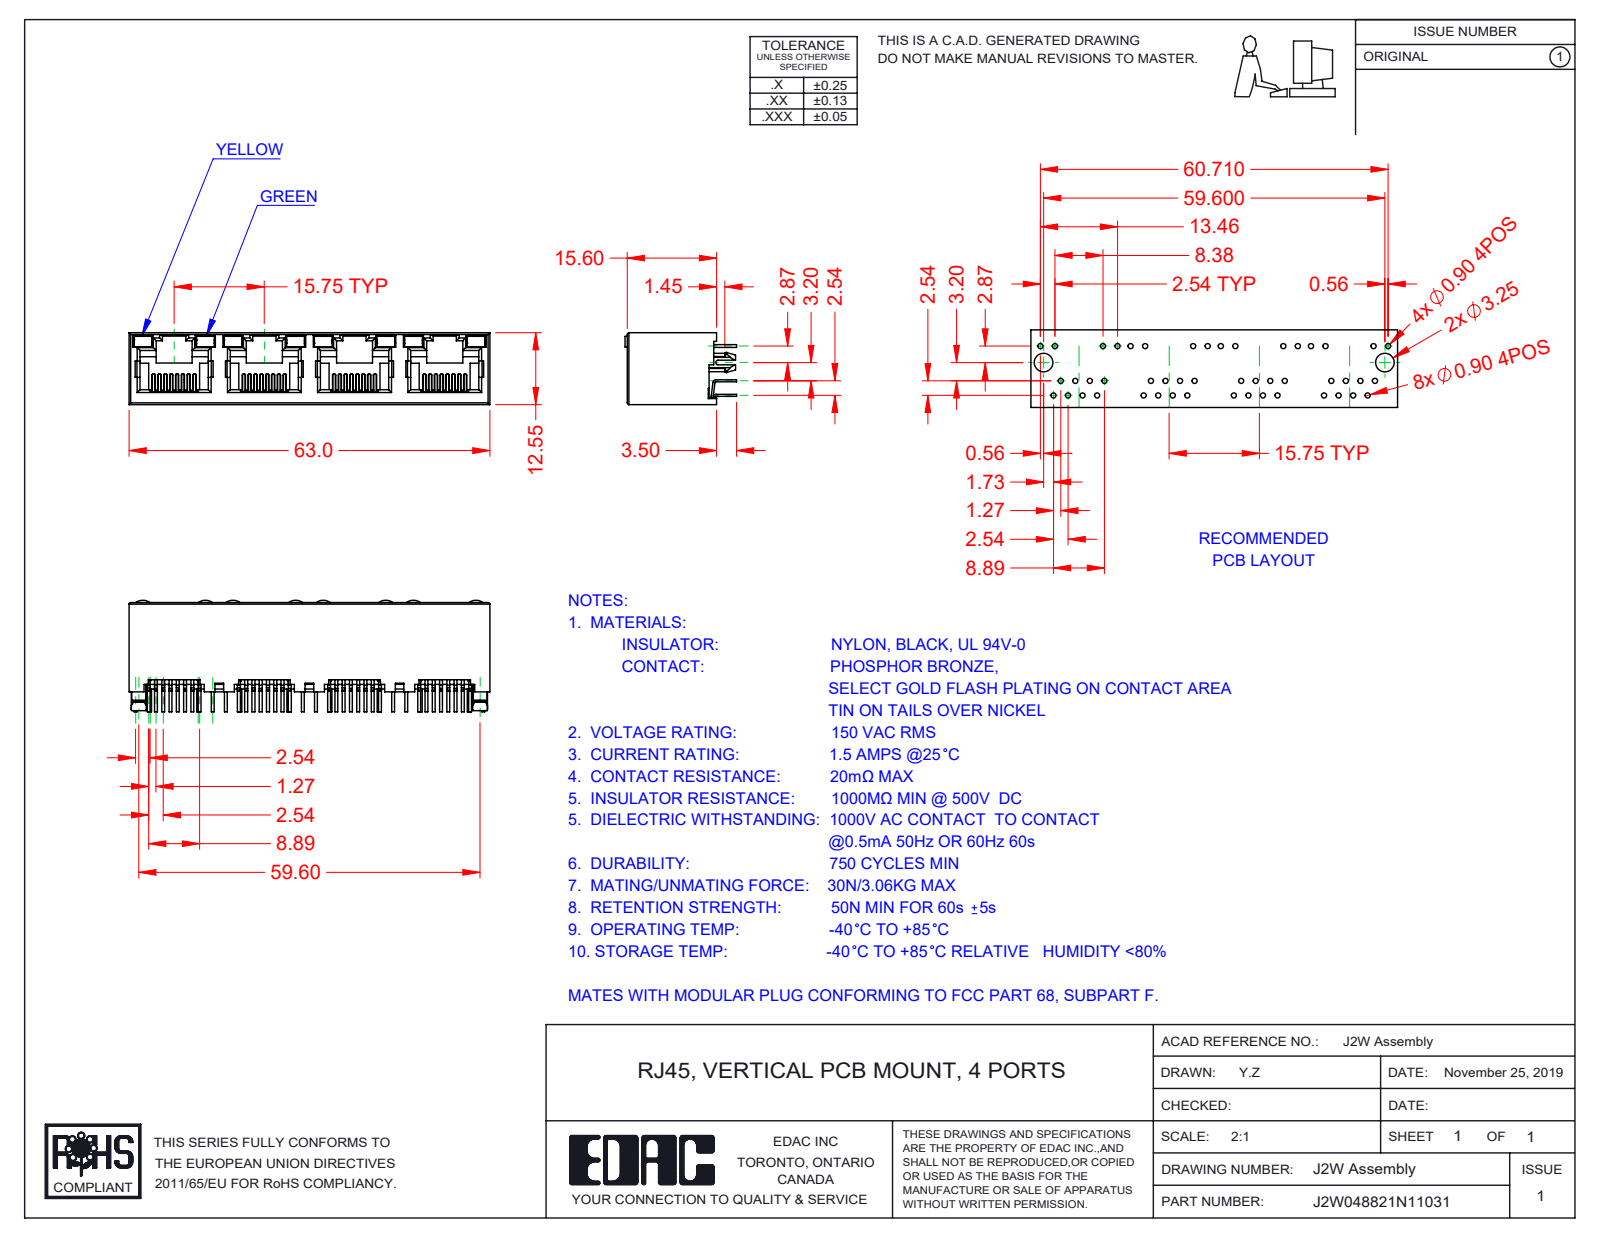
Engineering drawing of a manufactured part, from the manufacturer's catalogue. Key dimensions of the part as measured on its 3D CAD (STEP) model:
Part name (STEP PRODUCT): 2W LED RH_3-Green; 2W LED LH_1-Yellow; J2W048821N13131; 2W Contacts (+2 more)
STEP written by: SolidWorks 2016 (CONFIG_CONTROL_DESIGN)
Units: millimetres
Bodies: 45 solids, 3135 faces (2600 planar, 477 cylindrical, 58 other)
Overall size (bounding box): 63 × 19.5 × 12.55
Volume: 5 335 mm³ · Surface area: 13 144 mm²
Partial cylindrical surfaces — rounded edges, fillets, slot ends (radius × count): R0.15 ×64, R0.2 ×29, R0.5 ×28, R0.3 ×14, R0.45 ×8, R2 ×8, R0.25 ×2, R1.5 ×2
Main face-to-face distances: 12.55, 11.9, 0.65, 15.75, 0.36, 1.5, 0.78, 0.6, 11.3, 31.5
